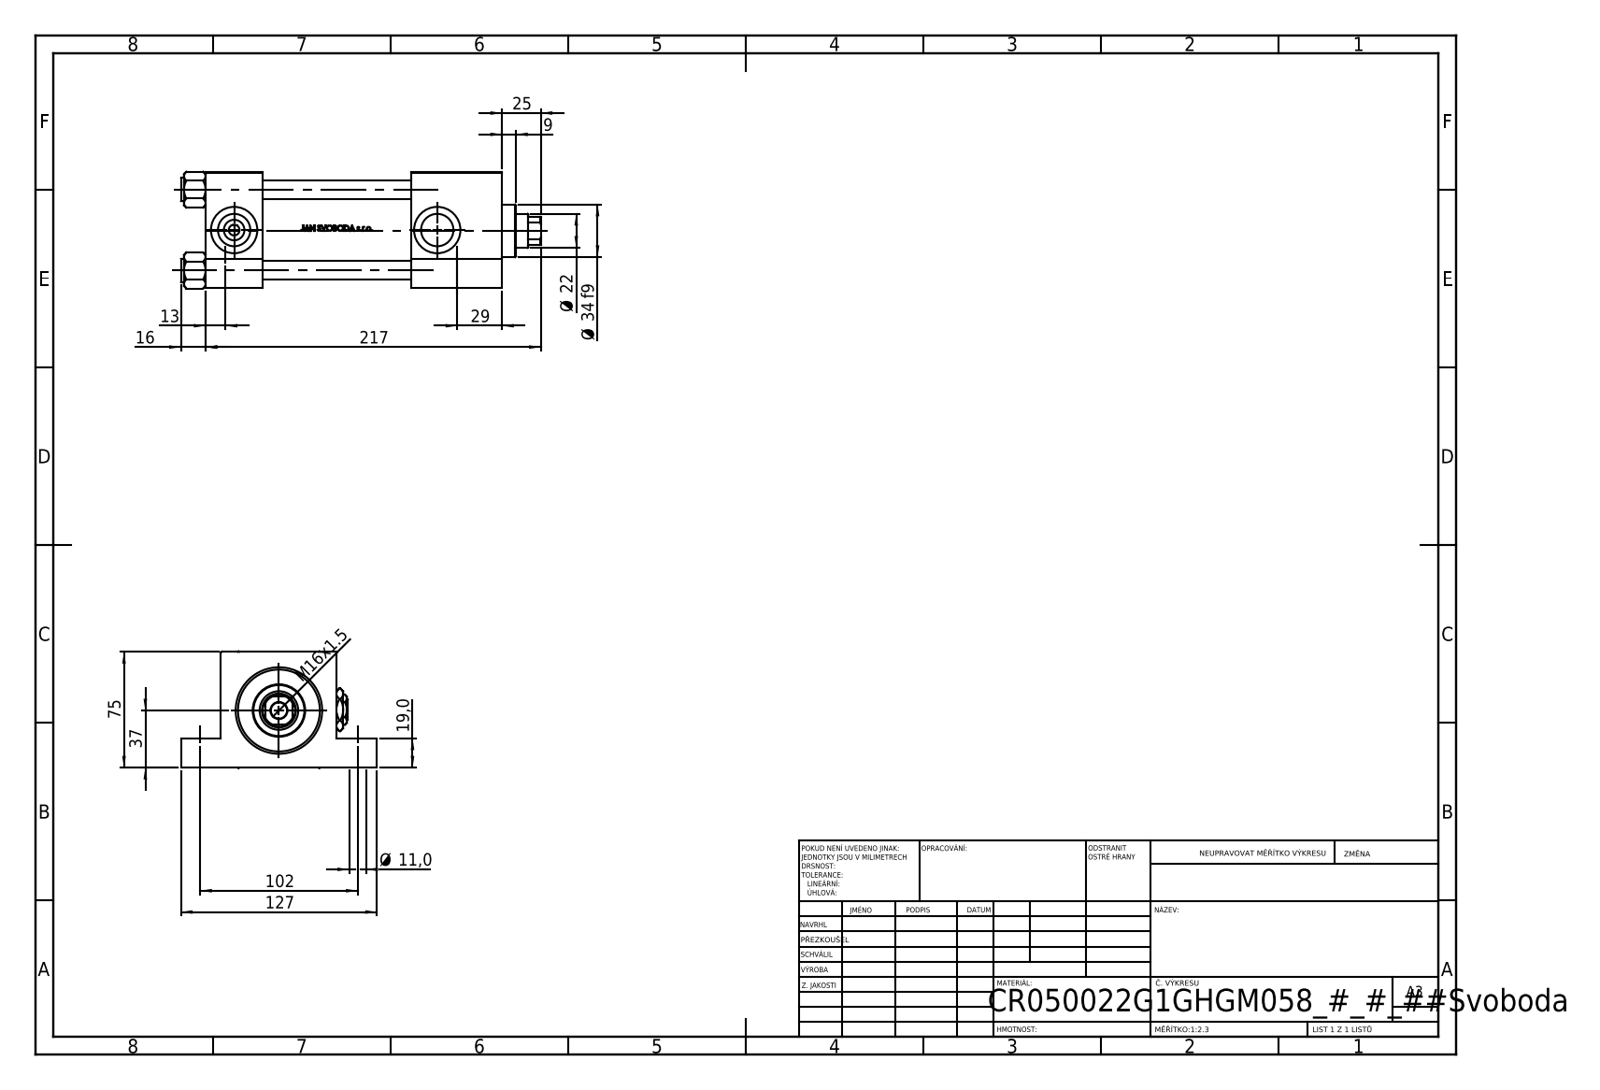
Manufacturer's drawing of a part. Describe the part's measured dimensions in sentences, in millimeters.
The part is named "V215CR_VCP_G; Zatka_pro_OIL_PORT; V215CR_G_Body; V215_VC_A (+2 more)". Its 3-D file was written by "SolidWorks 2019 (CONFIG_CONTROL_DESIGN)". It is 12 solids with 1134 faces: 454 planar, 128 cylindrical and 552 other. Overall it measures 233 by 127 by 75.54 millimeters. Its volume is 803 020 cubic millimeters and its surface area 182 315 square millimeters. Round holes: 4 of diameter 11, 4 of diameter 12, 2 of diameter 7, 2 of diameter 20.96, 2 of diameter 30, 1 of diameter 10.5, 1 of diameter 22, 1 of diameter 25, 1 of diameter 41, 1 of diameter 50, 1 of diameter 53. Round bosses or shafts: 4 of diameter 15, 1 of diameter 56, 1 of diameter 34. Partial cylindrical surfaces (rounded edges, fillets, slot ends): 1 of radius 10.5. The main face-to-face distances are 75, 37, 192, 155, 19, 56, 133, 96, 59, 26. The hole center spacings are 52.3, 36.63, 37.34, 73.96, 102, 150, 181.39, 131.5.
